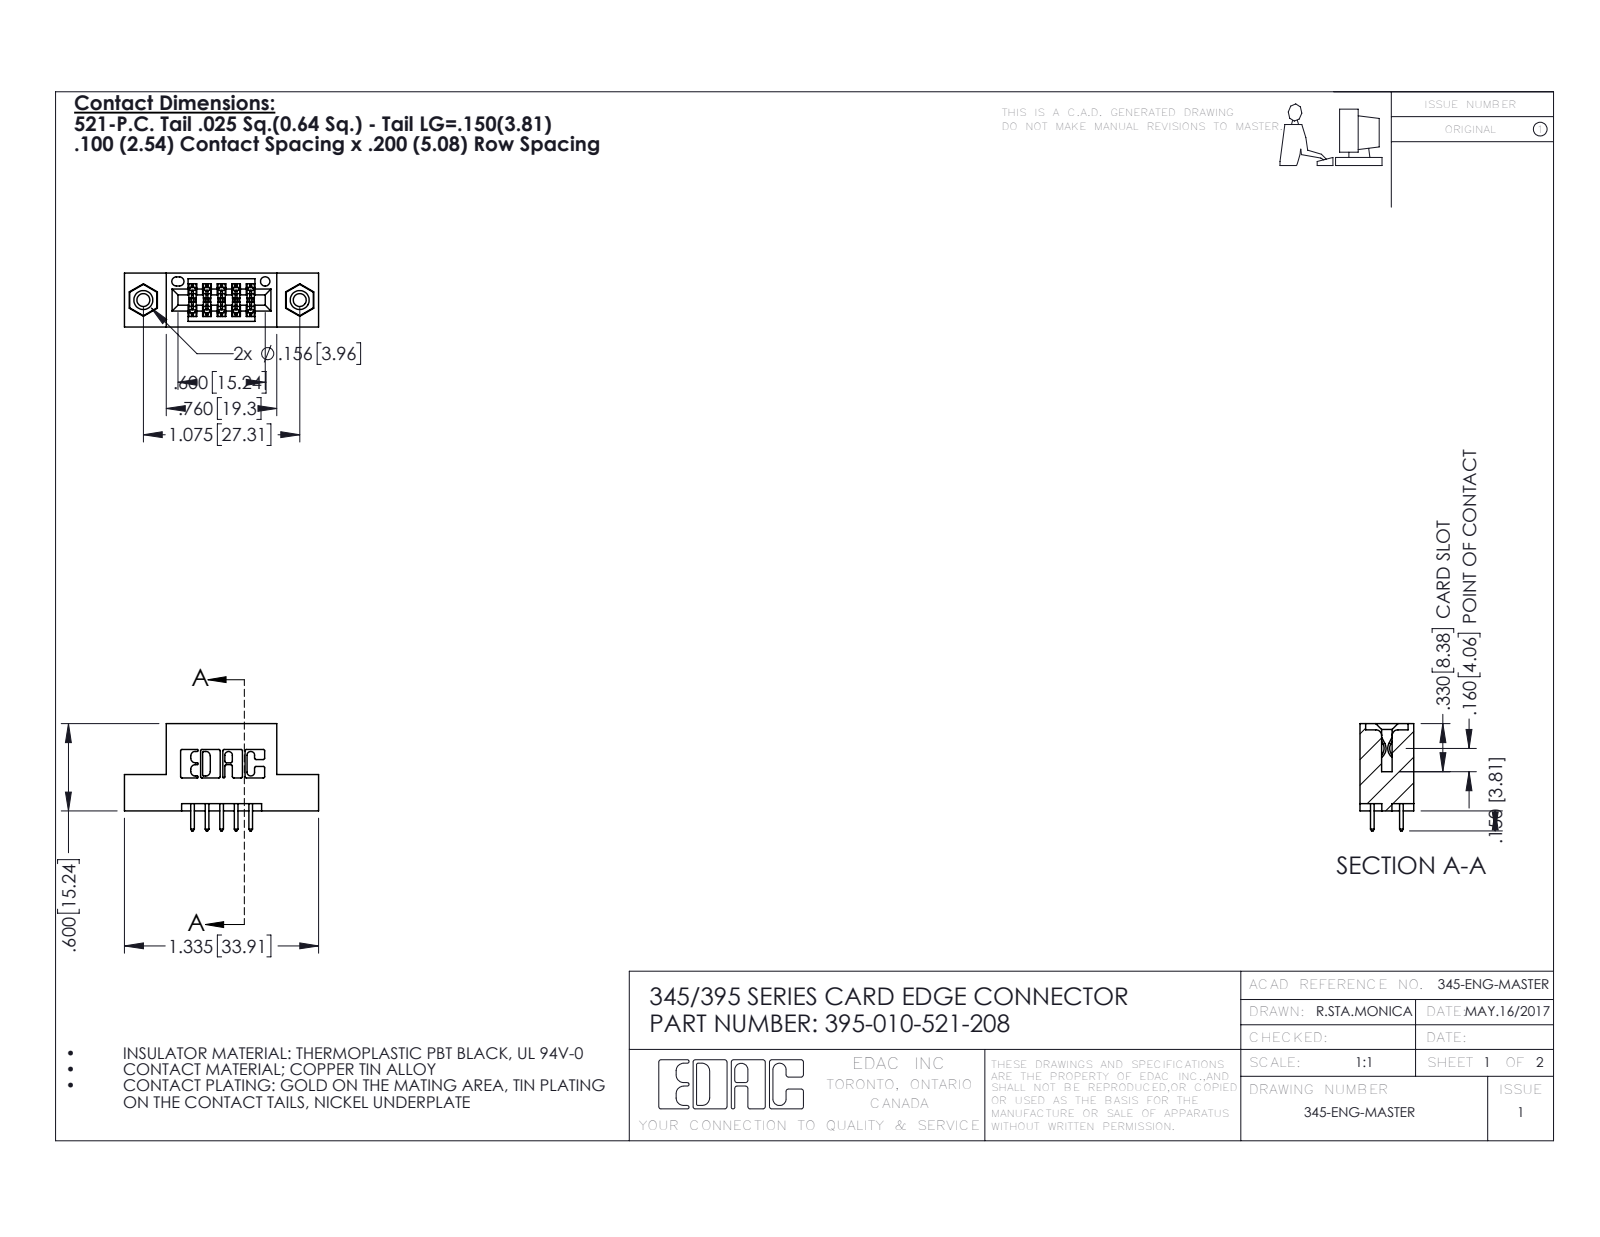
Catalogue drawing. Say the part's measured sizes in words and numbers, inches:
The part is named "345-250-001_345-250-003-102; 395-010-521-208; 345 Part_Flush Mounting Lugs - 0.156 Dia-TI; 345-292-001_345-293-121". Its 3-D file was written by "SolidWorks 2016 (CONFIG_CONTROL_DESIGN)". It is 13 solids with 686 faces: 442 planar, 228 cylindrical and 16 other. Overall it measures 1.335 by 0.737 by 0.37 inches. Its volume is 0.179 cubic inches and its surface area 5.605 square inches. Round holes: 2 of diameter 0.089, 2 of diameter 0.125, 2 of diameter 0.156, 1 of diameter 0.064. Round bosses or shafts: 2 of diameter 0.155. Partial cylindrical surfaces (rounded edges, fillets, slot ends): 22 of radius 0.01, 15 of radius 0.006, 10 of radius 0.01, 6 of radius 0.007, 6 of radius 0.031, 3 of radius 0.026, 2 of radius 0.014, 2 of radius 0.019. The main face-to-face distances are 0.2, 0.37, 0.072, 0.298, 0.1, 0.098, 0.272, 0.025, 0.35, 0.25. The hole center spacings are 0.27, 0.847, 1.075.
